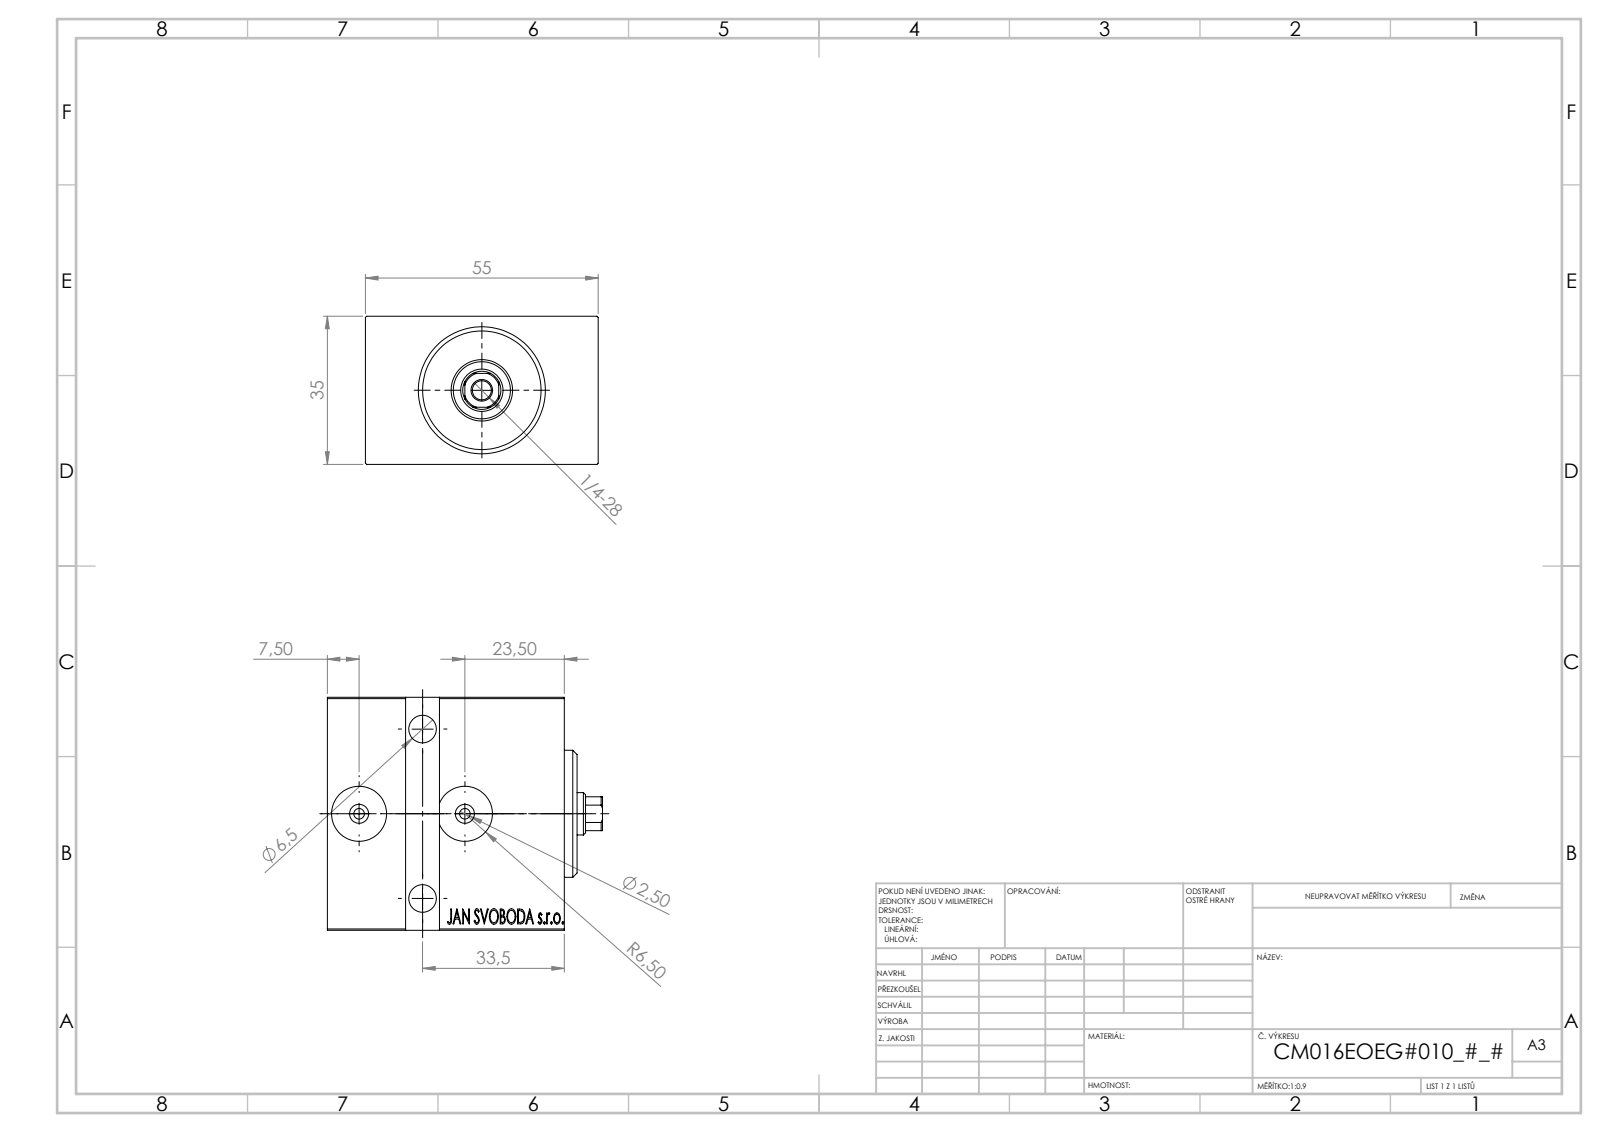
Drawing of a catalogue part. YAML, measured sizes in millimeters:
part_name: "V450CM_E_Body; V450CM_E_VCP; V450CM_VC_B"
step_written_by: "SolidWorks 2019 (CONFIG_CONTROL_DESIGN)"
units: millimeters
bodies: {solids: 3, faces: 852, planar: 411, cylindrical: 47, other: 394}
overall_size: [65, 55, 35]
volume: 105743
surface_area: 24598
round_holes:
  - {diameter: 2.5, count: 2}
  - {diameter: 6.5, count: 2}
  - {diameter: 10.5, count: 2}
  - {diameter: 13, count: 2}
  - {diameter: 4.5, count: 1}
  - {diameter: 10, count: 1}
  - {diameter: 13.5, count: 1}
  - {diameter: 14.5, count: 1}
  - {diameter: 16, count: 1}
  - {diameter: 25, count: 1}
round_bosses_or_shafts:
  - {diameter: 4.5, count: 2}
  - {diameter: 30, count: 1}
  - {diameter: 18, count: 1}
partial_cylinders:
  - {radius: 4.5, count: 1}
face_to_face_distances: [35, 55, 56, 5, 51, 8, 3, 1, 59, 46]
hole_center_spacings: [25, 22.36, 40]
